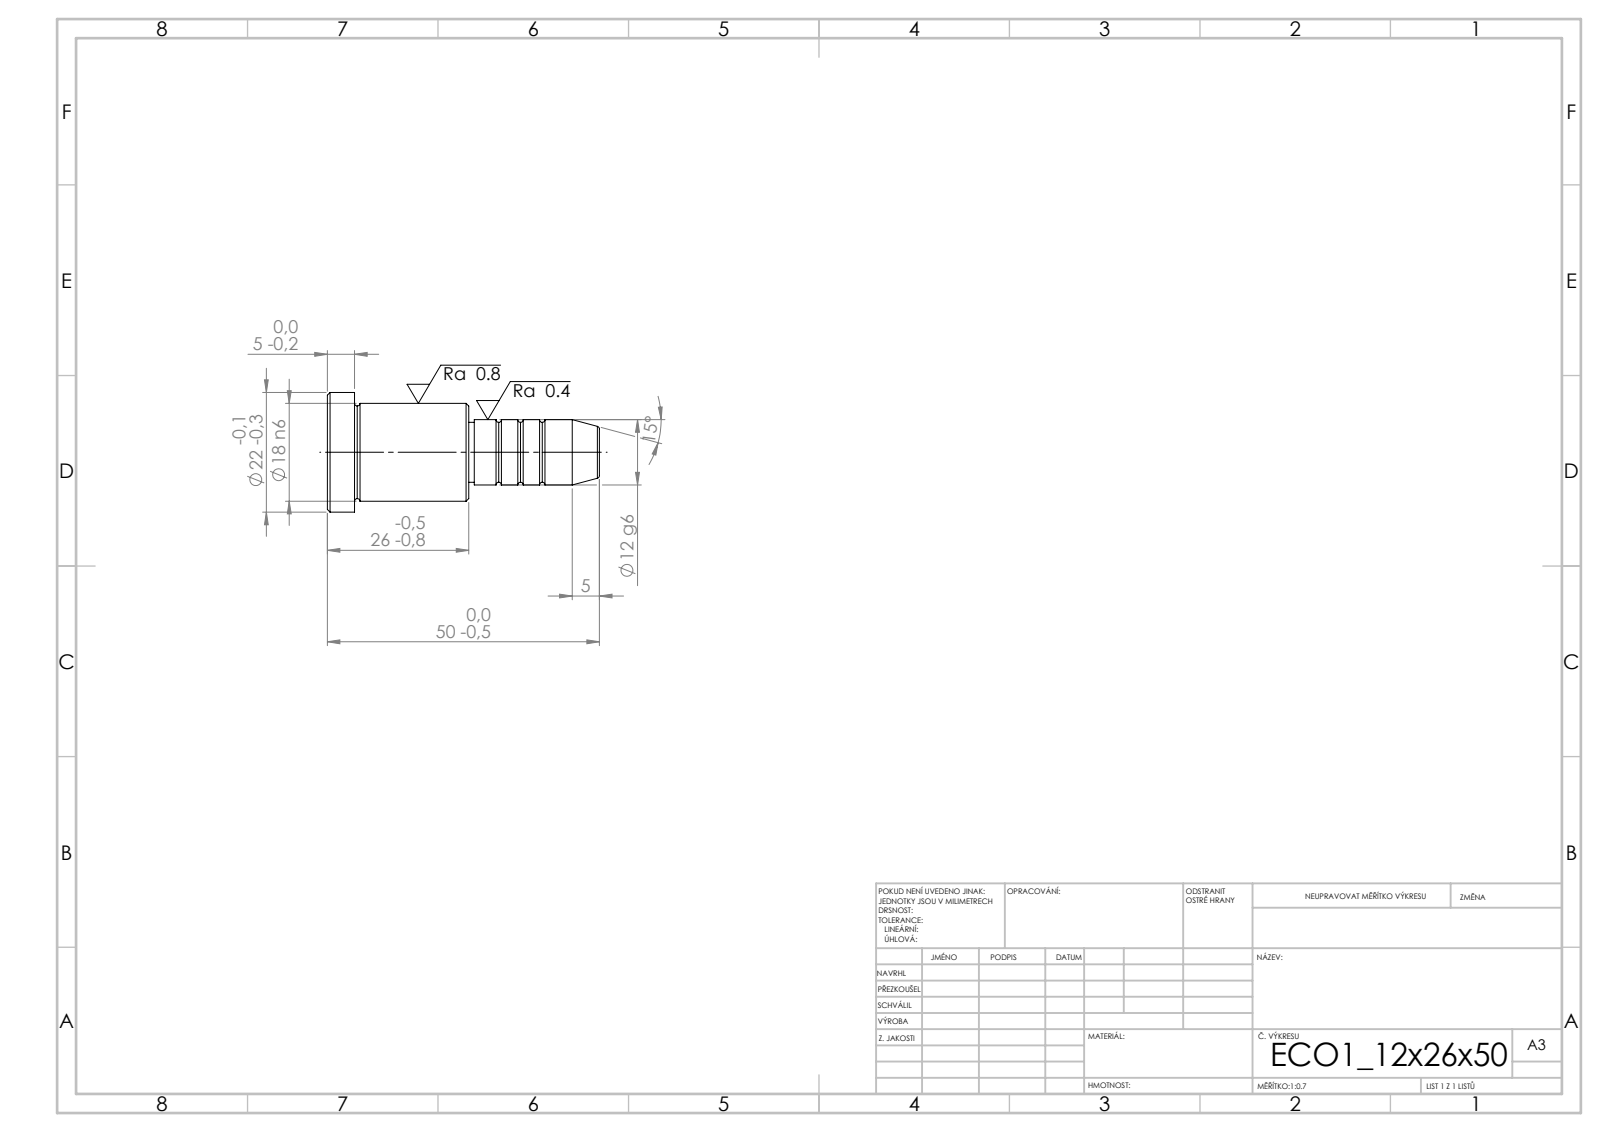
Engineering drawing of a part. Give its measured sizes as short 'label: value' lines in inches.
written by: SolidWorks 2019 (CONFIG_CONTROL_DESIGN)
unit: in
bodies: 1 solid, 43 faces (5 planar, 14 cylindrical, 24 other)
size: 1.969 × 0.866 × 0.866
volume: 0.595 in³; area: 4.983 in²
bosses: 1× ⌀0.866, 1× ⌀0.709, 1× ⌀0.472, 1× ⌀0.433
face distances: 1.024, 0.827, 0.197, 0.945, 1.772, 1.969, 0.906, 0.039, 0.866, 1.063
